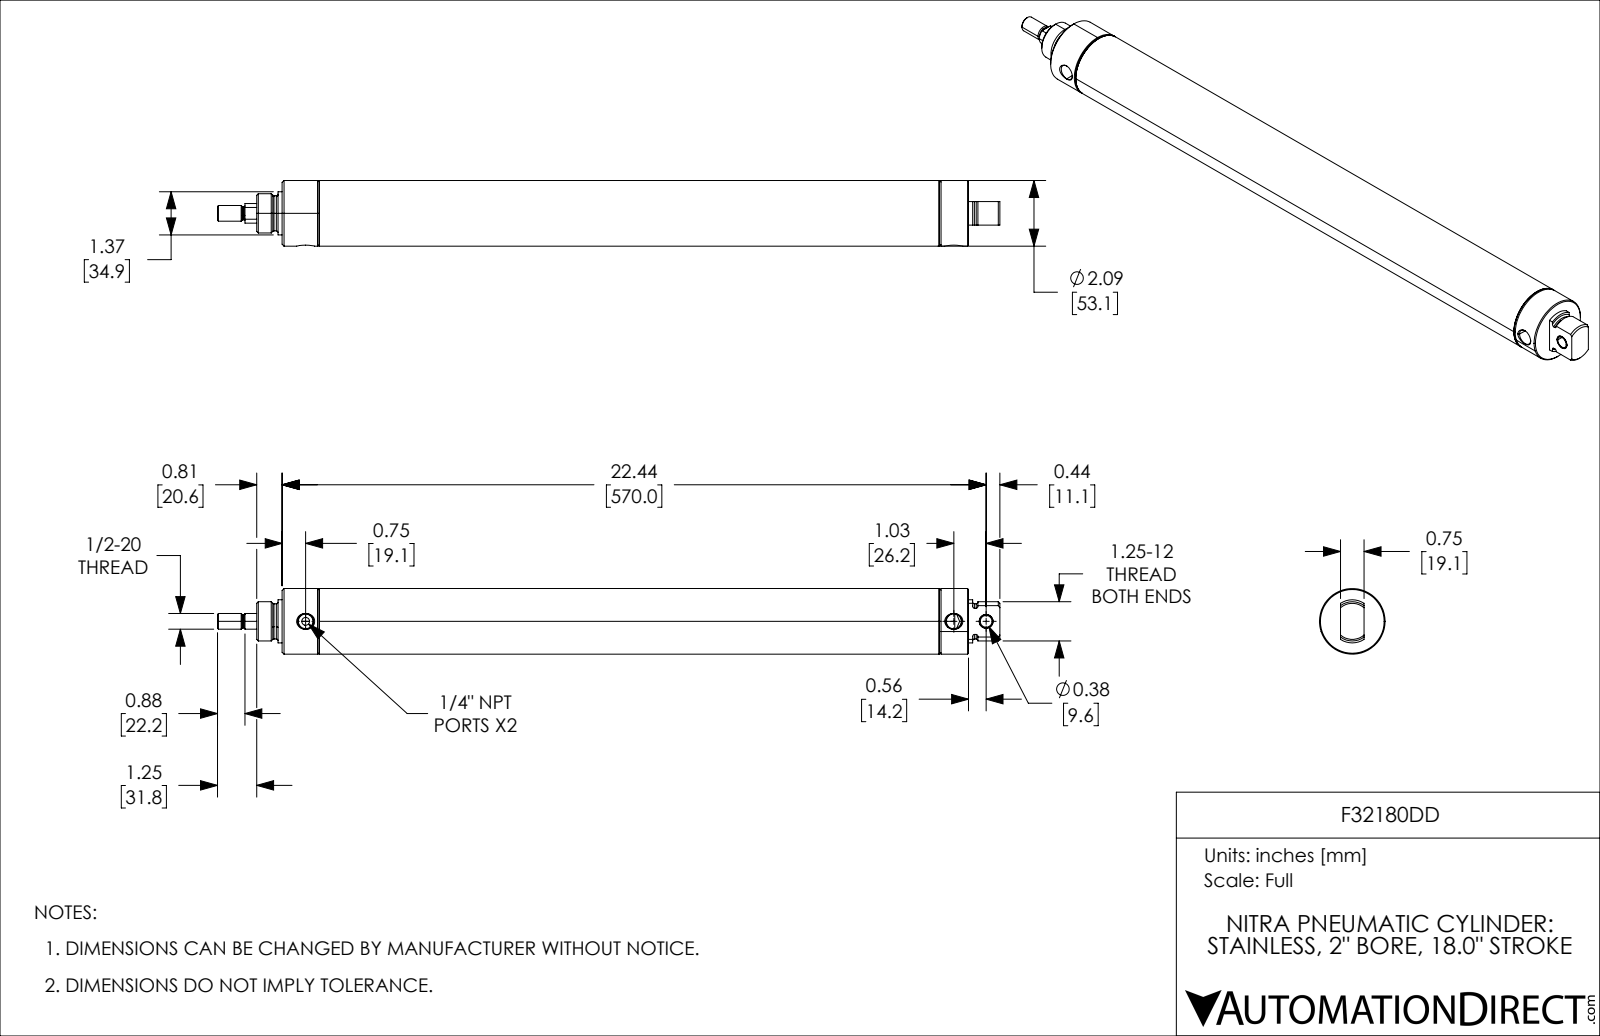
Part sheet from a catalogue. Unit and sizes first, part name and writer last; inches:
Units: inches
Overall size (bounding box): 24.938 × 2.09 × 2.09
Round holes (diameter × count): ⌀0.25 ×1, ⌀0.376 ×1, ⌀0.439 ×1, ⌀0.48 ×1, ⌀0.65 ×1, ⌀0.75 ×1, ⌀1.931 ×1
Round bosses / shafts (diameter × count): ⌀2.09 ×1, ⌀2.014 ×1, ⌀1.373 ×1, ⌀1.25 ×1, ⌀1.122 ×1, ⌀0.625 ×1, ⌀0.5 ×1, ⌀0.412 ×1
Partial cylindrical surfaces — rounded edges, fillets, slot ends (radius × count): R0.561 ×1
Main face-to-face distances: 1.188, 18, 19.188, 20.378, 2.378, 1.19, 19.188, 1.188, 1.19, 1.502
Hole centre spacings: 1.03, 20.66, 21.69
Volume: 24.32 in³ · Surface area: 363.6 in²
Bodies: 5 solids, 160 faces (31 planar, 60 cylindrical, 69 other)
Part name (STEP PRODUCT): F32180DD_11; F32180DD_7; F32180DD_9; F32180DD (+2 more)
STEP written by: SolidWorks 2021 (CONFIG_CONTROL_DESIGN)
